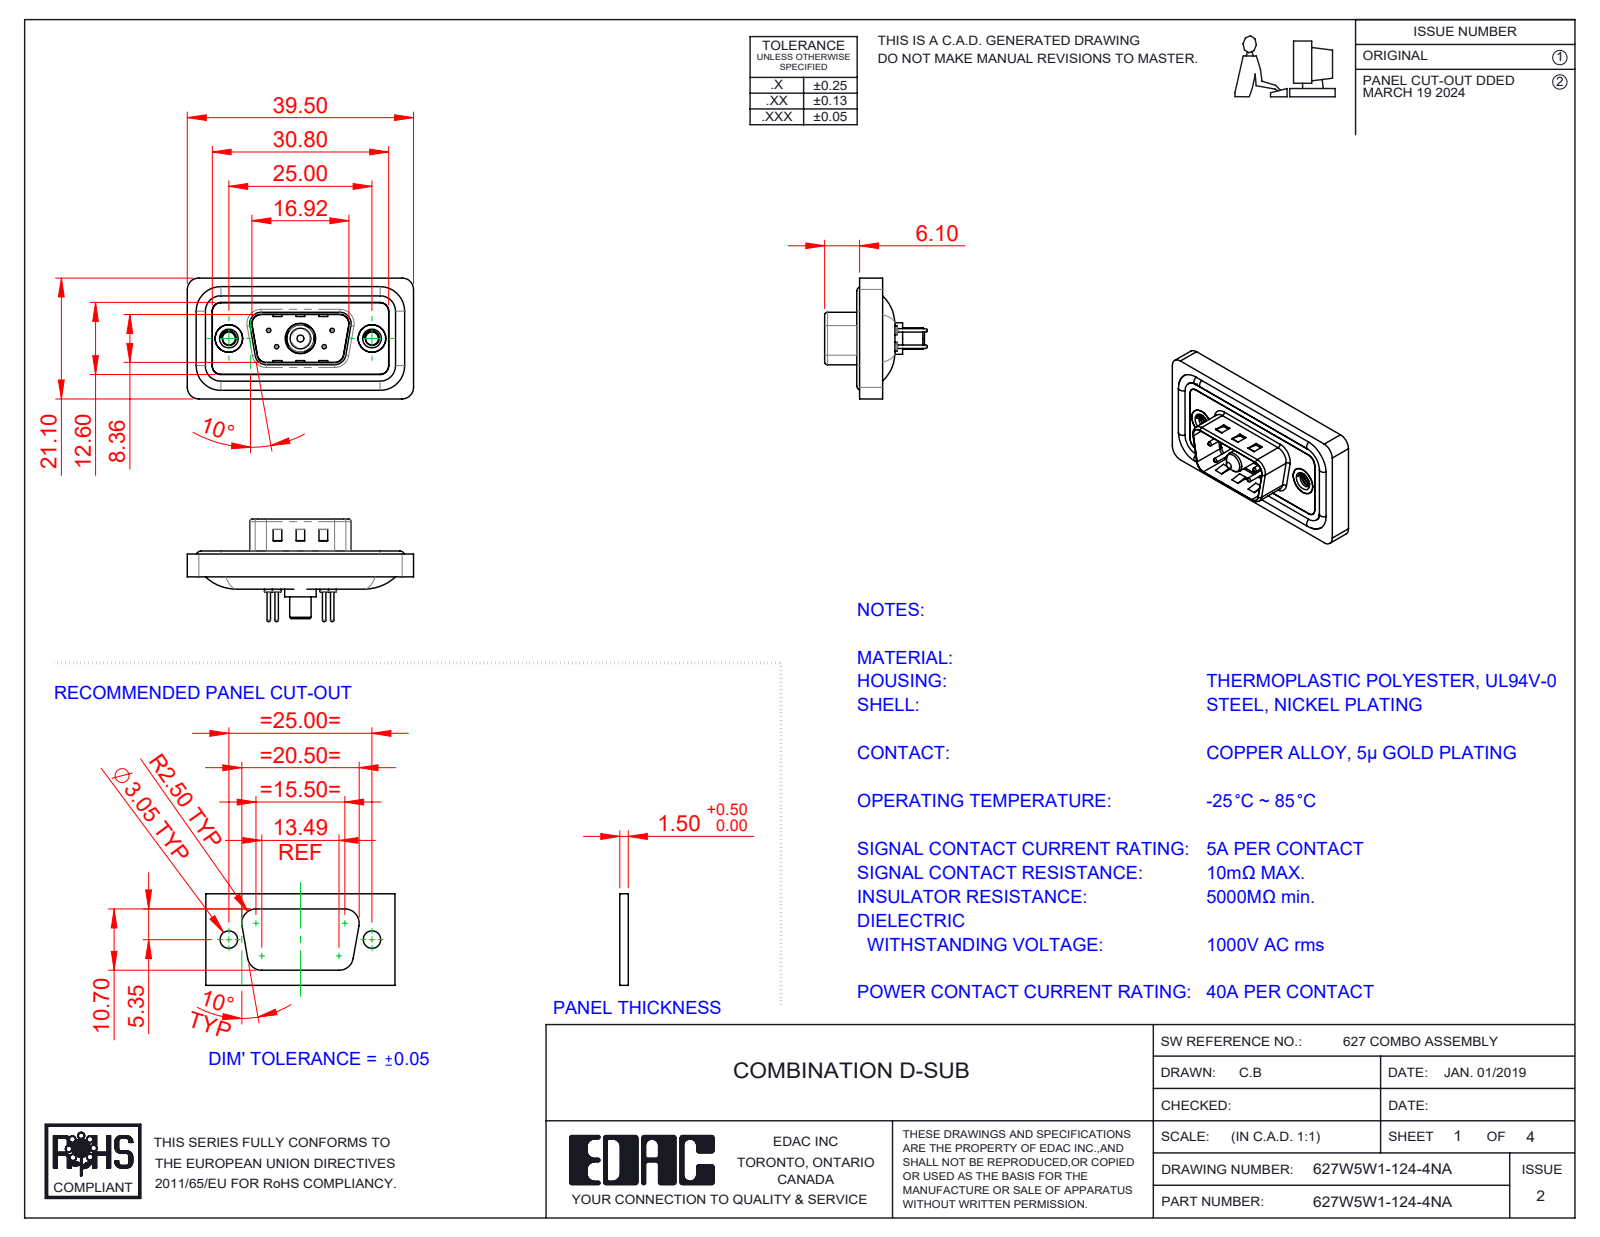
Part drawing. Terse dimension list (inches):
name: 627W5W1-124-4NA; 627Combo Waterproof Housing_09 Contacts; 627Combo Threaded Rivet_A; 627Combo Shell Rear_09 Contacts (+5 more)
written by: SolidWorks 2023 (CONFIG_CONTROL_DESIGN)
unit: in
bodies: 13 solids, 596 faces (183 planar, 257 cylindrical, 156 other)
size: 1.555 × 0.831 × 0.705
volume: 0.269 in³; area: 10.77 in²
holes: 4× ⌀0.03, 4× ⌀0.063, 4× ⌀0.079, 2× ⌀0.089, 2× ⌀0.157, 2× ⌀0.189, 2× ⌀0.197, 1× ⌀0.191, 1× ⌀0.209
bosses: 4× ⌀0.063, 4× ⌀0.059, 4× ⌀0.024, 2× ⌀0.193, 1× ⌀0.217, 1× ⌀0.205, 1× ⌀0.187, 1× ⌀0.148
rounds: 22× R0.059, 18× R0.079, 8× R0.02, 8× R0.063, 4× R0.01, 4× R0.024, 4× R0.026, 4× R0.035
face distances: 0.016, 0.043, 0.114, 0.063, 0.122, 0.02, 0.059, 0.098, 0.157, 0.031
hole spacings: 0.124, 0.225, 0.28, 0.492, 0.713, 0.173, 0.173, 0.327
